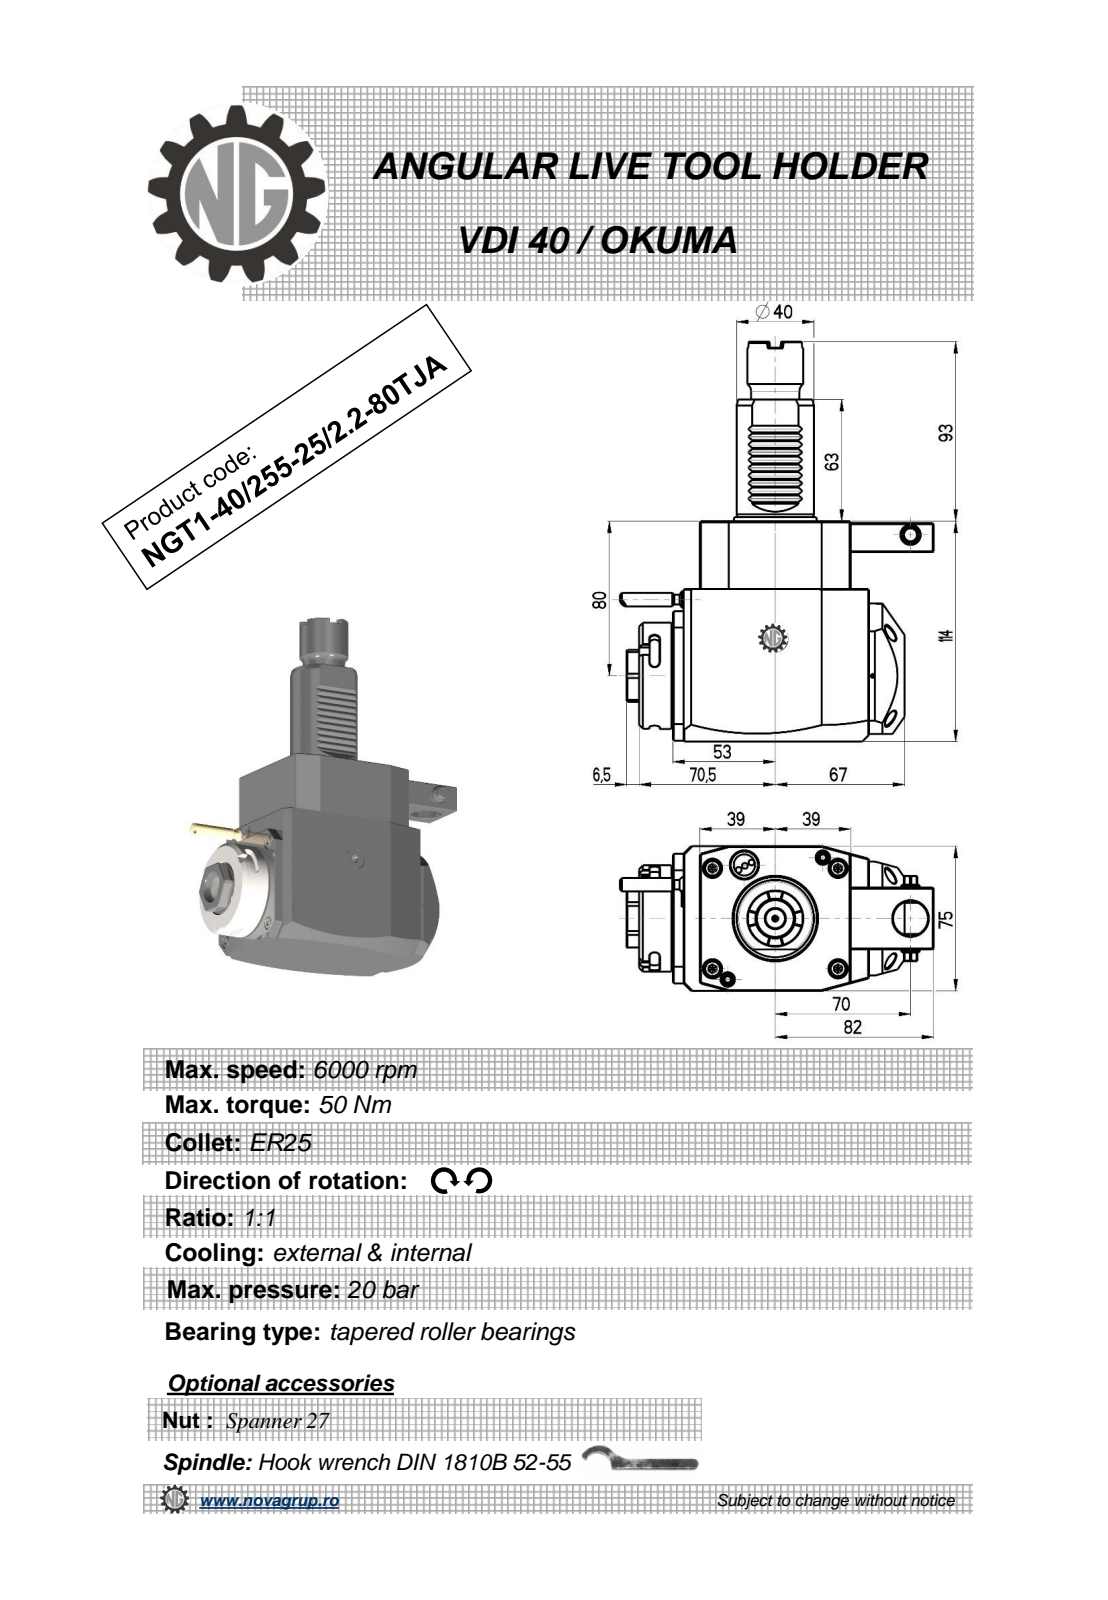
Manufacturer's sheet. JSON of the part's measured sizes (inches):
{"part_name": "NGT1_40_255_25_1_2_80TJA", "step_written_by": "PRO/ENGINEER BY PARAMETRIC TECHNOLOGY CORPORATION, 2010280 (CONFIG_CONTROL_DESIGN)", "units": "inches", "bodies": {"solids": 1, "faces": 386, "planar": 196, "cylindrical": 84, "other": 106}, "overall_size": [8.15, 6.391, 2.953], "volume_in3": 59.85, "surface_area_in2": 116.5, "round_holes": [[0.709, 2], [0.098, 1], [0.118, 1], [0.374, 1]], "round_bosses_or_shafts": [[0.353, 2], [2.165, 1], [1.89, 1], [1.575, 1], [1.142, 1], [0.984, 1], [0.394, 1], [0.276, 1]], "partial_cylinders_radius": [[0.012, 10], [0.098, 6], [7.087, 2], [0.02, 1], [0.152, 1], [0.167, 1], [0.394, 1], [0.591, 1]], "face_to_face_distances": [2.953, 4.488, 0.551, 0.689, 4.311, 3.11, 3.622, 3.071, 1.24, 3.858], "hole_center_spacings": [1.47, 1.701, 2.854]}
